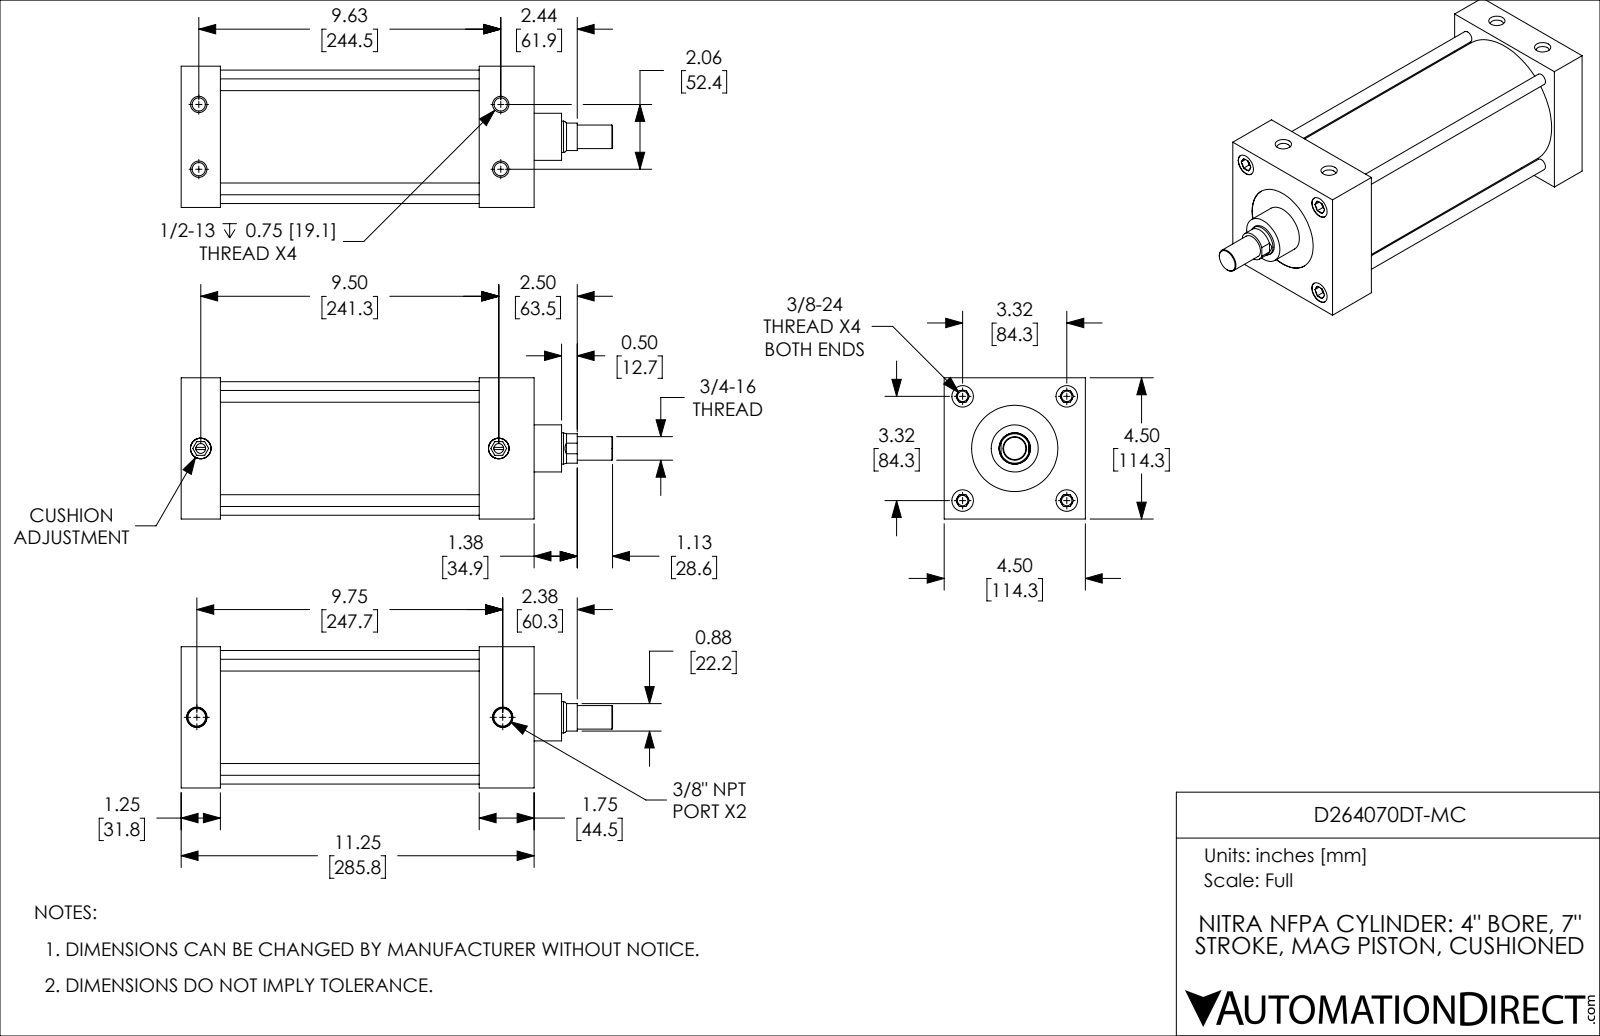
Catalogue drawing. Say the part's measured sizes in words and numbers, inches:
The part is named "D264070DT-MC_BODY; D264070DT-MC_PISTON_KK1; D264070DT-MC_CUSHION; D264070DT-MC". Its 3-D file was written by "SolidWorks 2019 (CONFIG_CONTROL_DESIGN)". It is 4 solids with 246 faces: 90 planar, 78 cylindrical and 78 other. Overall it measures 13.75 by 4.5 by 4.5 inches. Its volume is 98.9 cubic inches and its surface area 493.2 square inches. Round holes: 4 of diameter 0.332, 4 of diameter 0.422, 4 of diameter 0.687, 2 of diameter 0.312, 2 of diameter 0.562, 2 of diameter 0.656, 1 of diameter 1.001, 1 of diameter 2.75, 1 of diameter 4.001. Round bosses or shafts: 4 of diameter 0.375, 2 of diameter 0.657, 1 of diameter 4.251, 1 of diameter 3.999, 1 of diameter 1.5, 1 of diameter 0.999, 1 of diameter 0.75. Partial cylindrical surfaces (rounded edges, fillets, slot ends): 1 of radius 0.469. The main face-to-face distances are 1.25, 4.5, 9.5, 8.25, 11.25, 10, 1.75, 2.5, 7, 8.75. The hole center spacings are 1.033, 2.347, 3.32, 9.742, 2.062, 4.695, 9.625, 9.843.
